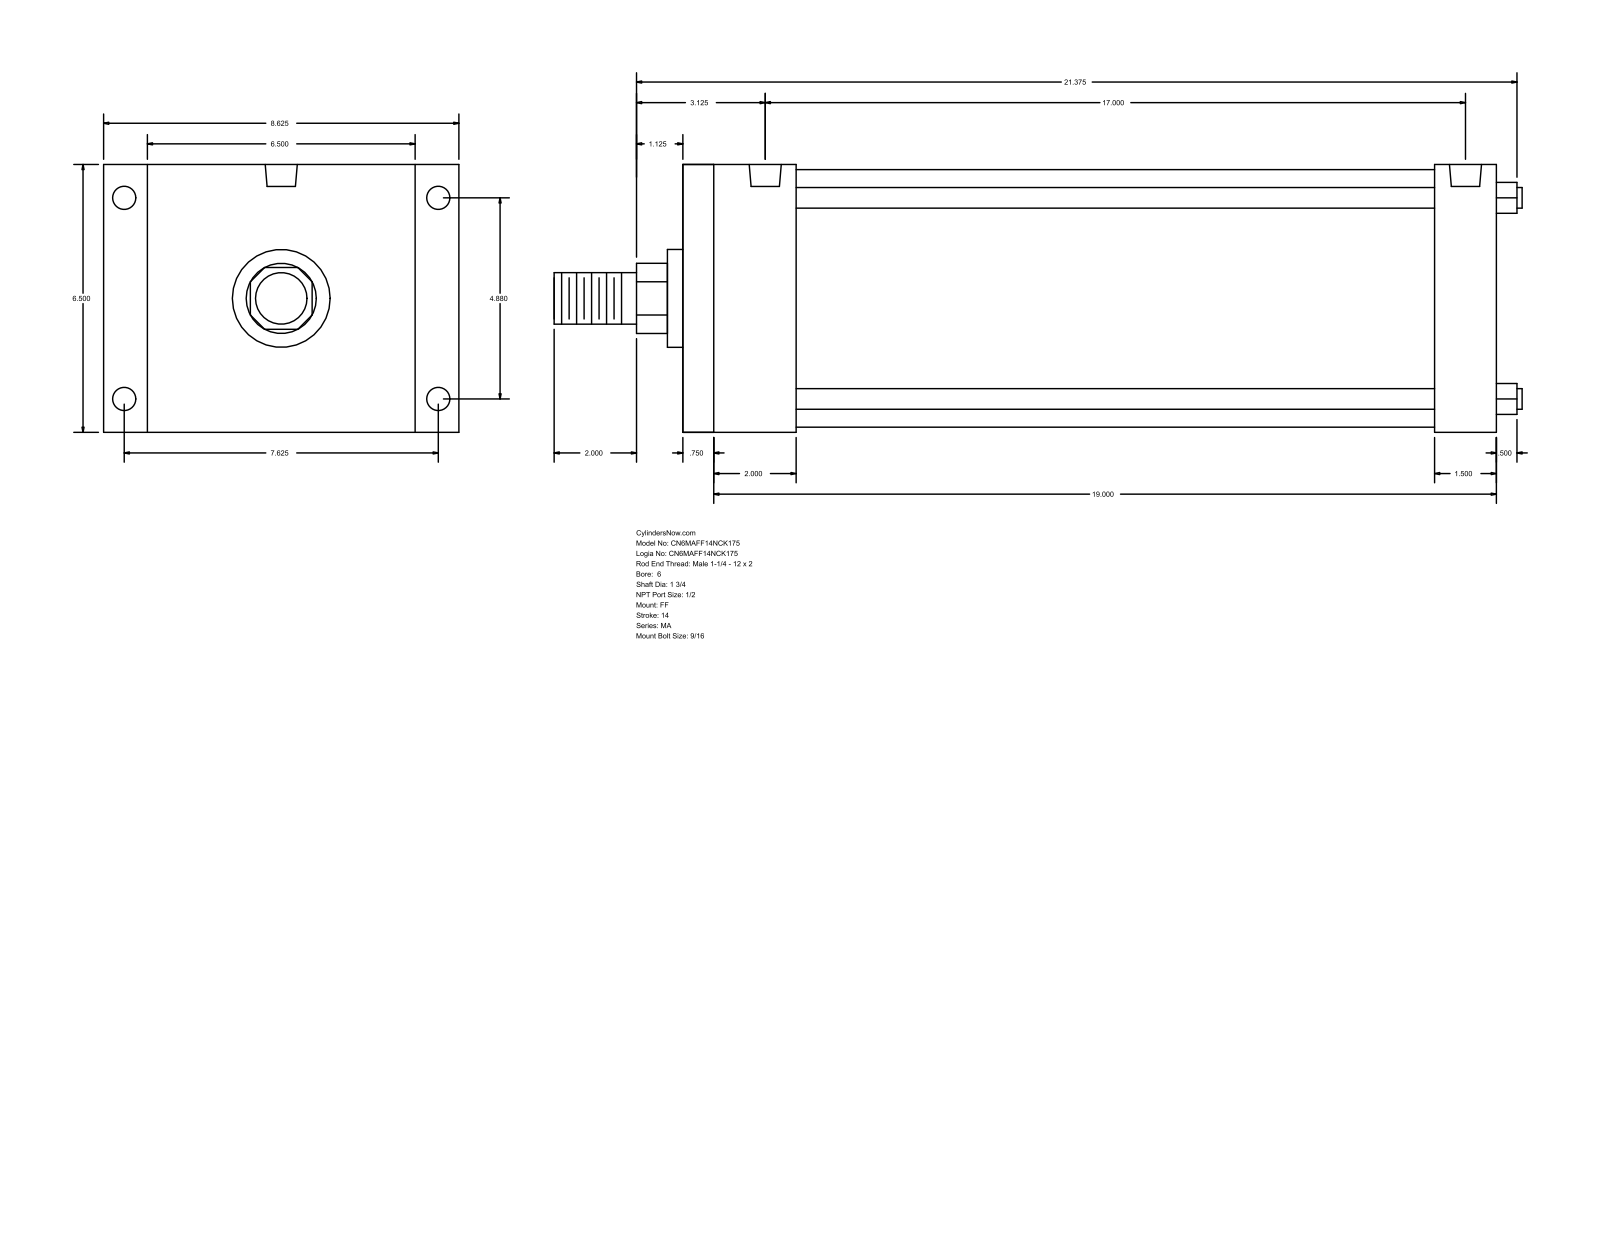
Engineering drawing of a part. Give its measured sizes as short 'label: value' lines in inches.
name: MA_FF__0600_1.75
written by: GSSL Pune (CONFIG_CONTROL_DESIGN)
unit: in
bodies: 0 solids, 92 faces (64 planar, 28 cylindrical, 0 other)
size: 23.5 × 8.625 × 6.5
holes: 4× ⌀0.563, 4× ⌀0.687, 2× ⌀0.778
bosses: 4× ⌀0.5, 1× ⌀6.25, 1× ⌀2.375, 1× ⌀1.75, 1× ⌀1.25
rounds: 1× R0.852
face distances: 6.5, 19.75, 0.75, 19, 2, 2.75, 17.5, 17, 18.25, 15.5
hole spacings: 4.88, 7.625, 9.053, 17
